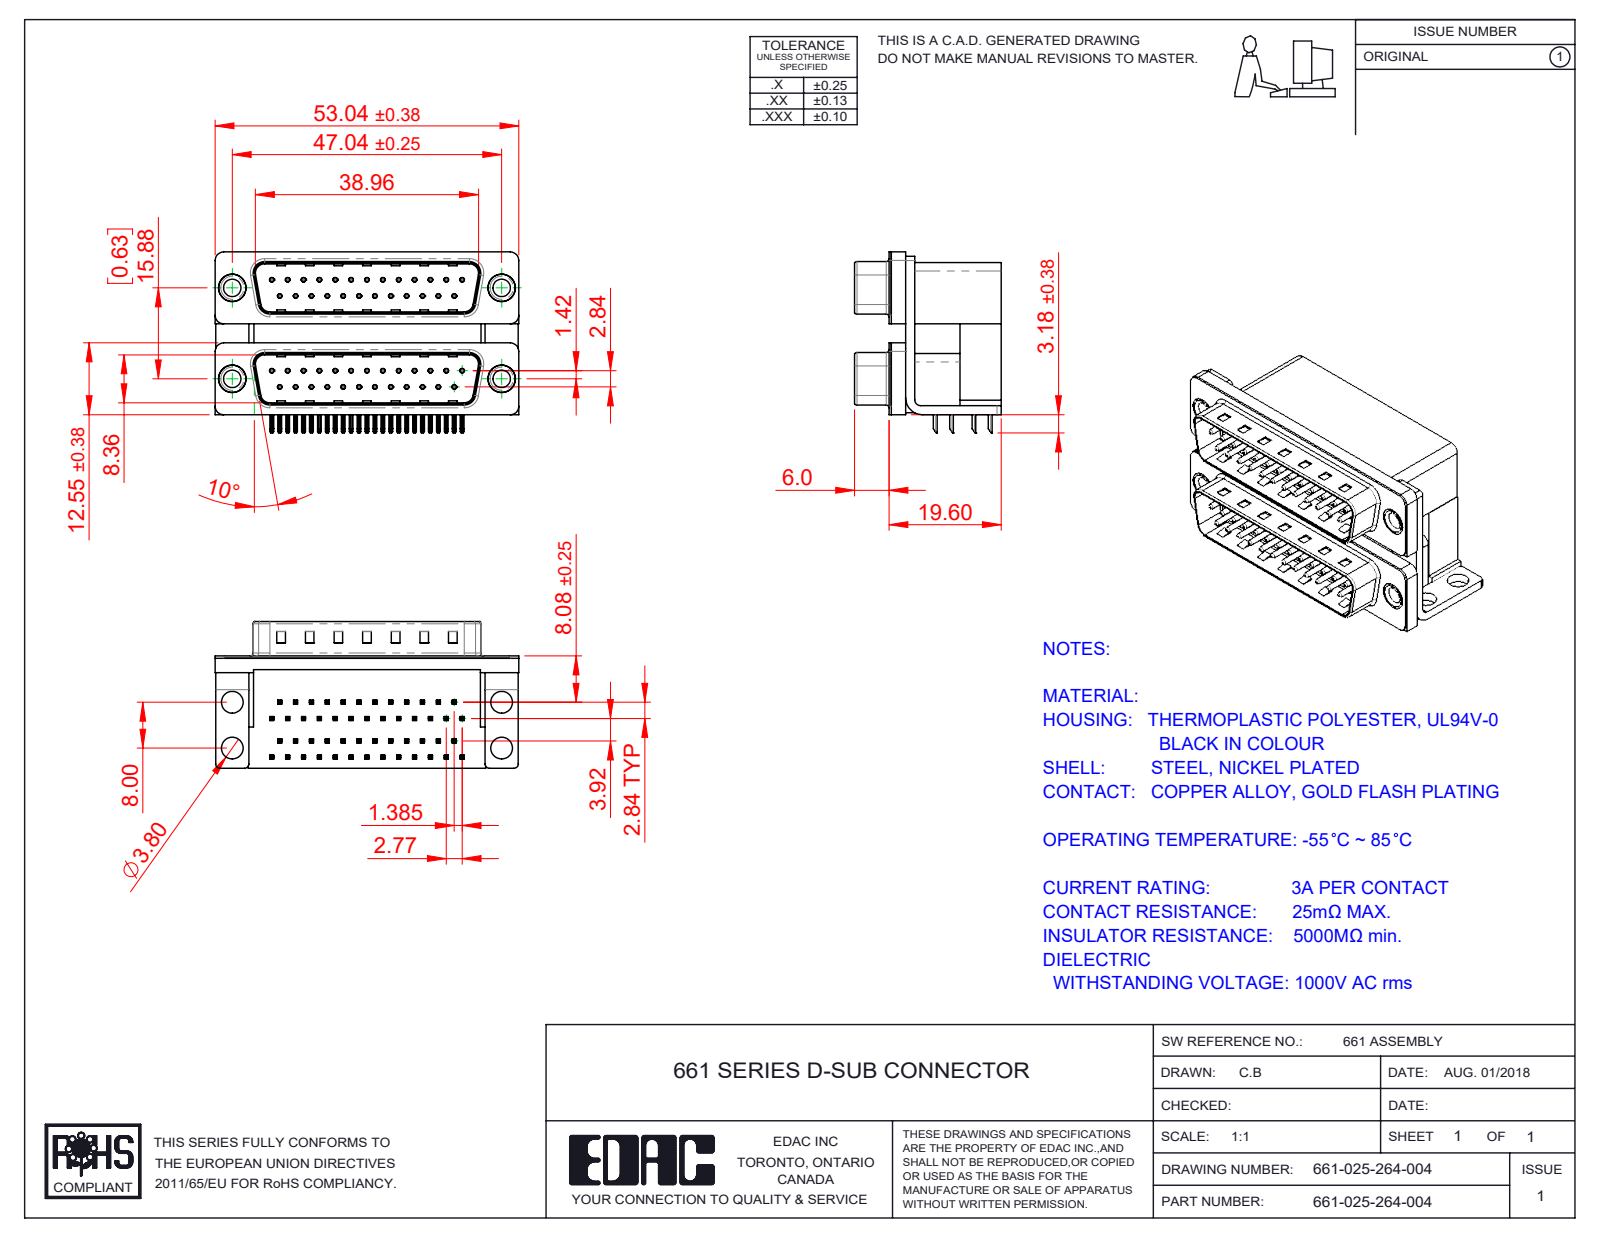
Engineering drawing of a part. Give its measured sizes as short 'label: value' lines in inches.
name: 661 Housing Spacer_25 Contacts L; 661 Contact Top Lower; 661 Contact Bottom Lower; 661 Housing Lower_25 Contacts (+7 more)
written by: SolidWorks 2020 (CONFIG_CONTROL_DESIGN)
unit: in
bodies: 61 solids, 4510 faces (2934 planar, 1230 cylindrical, 346 other)
size: 2.088 × 1.244 × 1.008
volume: 1.223 in³; area: 32.15 in²
holes: 50× ⌀0.014, 50× ⌀0.031, 4× ⌀0.12, 4× ⌀0.138, 4× ⌀0.157, 4× ⌀0.189, 4× ⌀0.197
bosses: 50× ⌀0.03, 4× ⌀0.193, 4× ⌀0.187, 4× ⌀0.152
rounds: 200× R0.01, 100× R0.005, 16× R0.02, 13× R0.059, 8× R0.035, 8× R0.063, 8× R0.079, 4× R0.016
face distances: 0.016, 0.756, 0.283, 0.472, 0.625, 0.421, 0.657, 0.374, 0.098, 0.611
hole spacings: 0.124, 0.109, 0.218, 0.327, 0.436, 0.545, 0.654, 0.198
